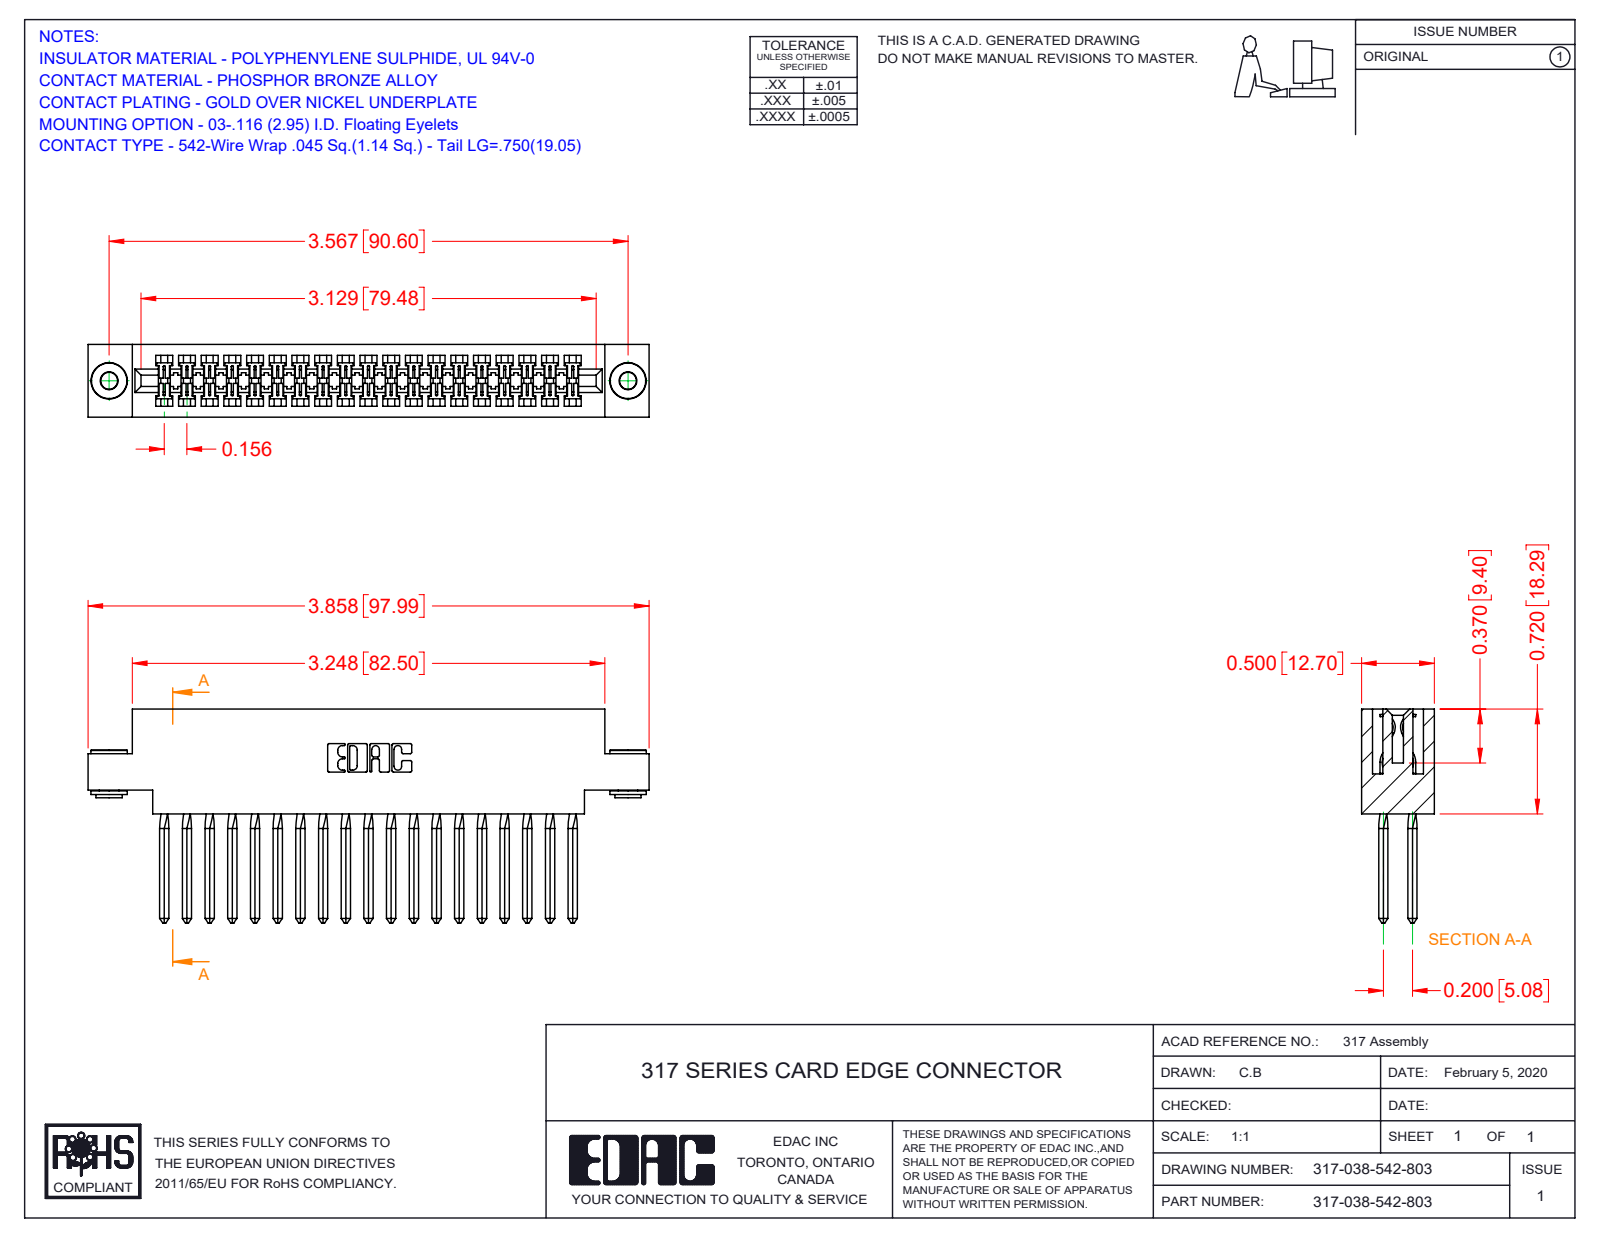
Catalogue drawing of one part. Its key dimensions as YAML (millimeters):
part_name: "317-290-003_542; 345-250-002_345-250-002-102; 317 Part_.156 Dia - TH; 317-038-542-803"
step_written_by: "SolidWorks 2016 (CONFIG_CONTROL_DESIGN)"
units: millimeters
bodies: {solids: 41, faces: 2306, planar: 1816, cylindrical: 330, other: 160}
overall_size: [98, 37.3, 12.7]
volume: 15300
surface_area: 20810
round_holes:
  - {diameter: 2.9, count: 2}
  - {diameter: 4, count: 2}
round_bosses_or_shafts:
  - {diameter: 6.4, count: 2}
  - {diameter: 4.6, count: 2}
  - {diameter: 3.5, count: 2}
partial_cylinders:
  - {radius: 0.2, count: 76}
  - {radius: 0.3, count: 22}
  - {radius: 0.2, count: 6}
  - {radius: 0.8, count: 6}
  - {radius: 0.7, count: 3}
  - {radius: 1.9, count: 2}
  - {radius: 2.3, count: 2}
  - {radius: 2.5, count: 2}
face_to_face_distances: [12.7, 1.9, 10.8, 2.8, 8.9, 5.1, 2.9, 3.5, 18.3, 1.2]
hole_center_spacings: [90.6]
